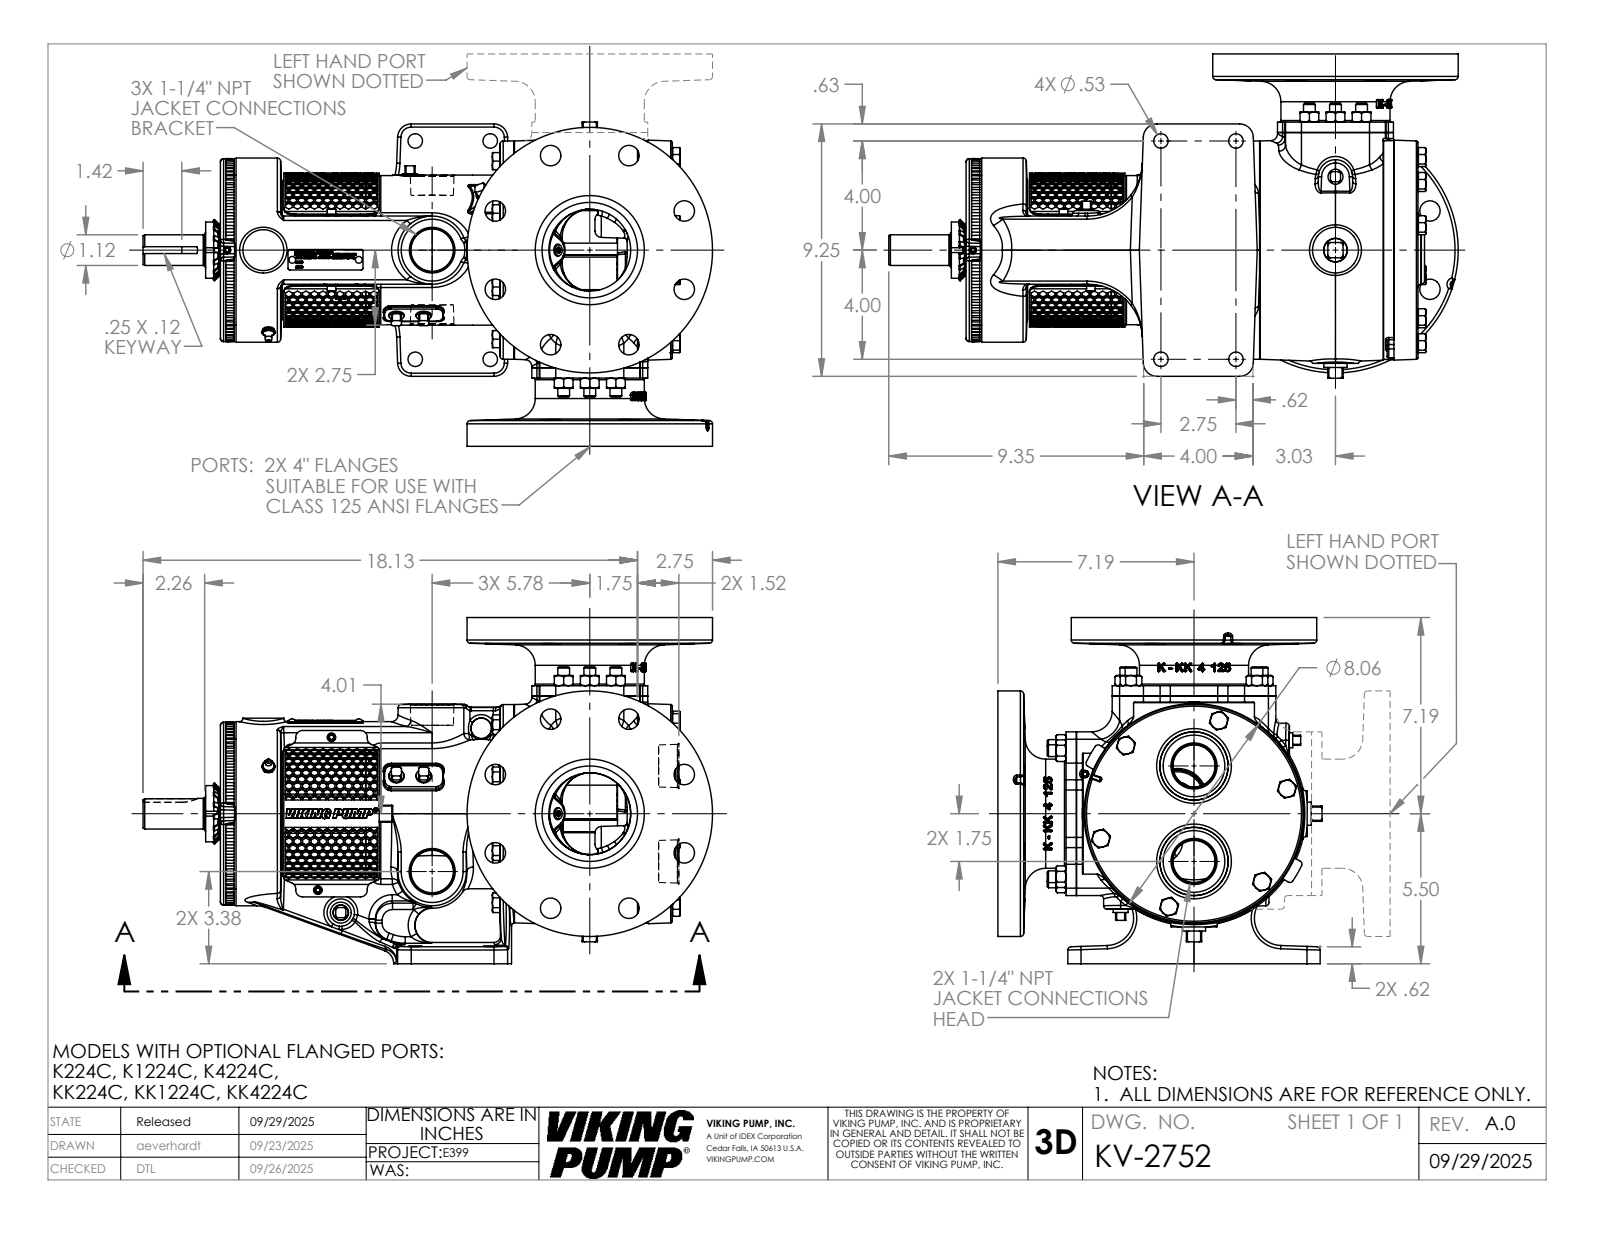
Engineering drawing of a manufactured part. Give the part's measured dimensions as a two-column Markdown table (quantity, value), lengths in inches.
| quantity | value |
| --- | --- |
| part name | KV-2752 |
| STEP written by | SolidWorks 2024 (AUTOMOTIVE_DESIGN) |
| units | inches |
| bodies | 1 solid, 4190 faces (1389 planar, 551 cylindrical, 2250 other) |
| overall size | 20.879 × 12.69 × 11.885 |
| volume | 745.6 in³ |
| surface area | 1 297 in² |
| round holes (diameter × count) | 0.75 × 16, 0.25 × 9, 0.78 × 8, 0.197 × 6, 0.531 × 4, 0.159 × 2, 0.313 × 2, 3 × 2, 4 × 2, 0.257 × 1, 0.453 × 1, 1.387 × 1 |
| round bosses / shafts (diameter × count) | 0.431 × 12, 0.625 × 11, 0.625 × 3, 0.312 × 3, 0.19 × 3, 9 × 2, 8 × 1, 6.75 × 1 |
| partial cylindrical surfaces (radius × count) | 0.12 × 44, 0.24 × 22, 0.03 × 20, 1 × 18, 0.12 × 16, 0.06 × 15, 0.25 × 8, 0.5 × 8 |
| main face-to-face distances | 12.69, 11.245, 2.5, 5.324, 16.569, 2.914, 5.94, 0.574, 4.75, 15.995 |
| hole center spacings | 2.87, 3.75, 5.303, 6.929, 3, 1.03, 4.994, 5.438 |
